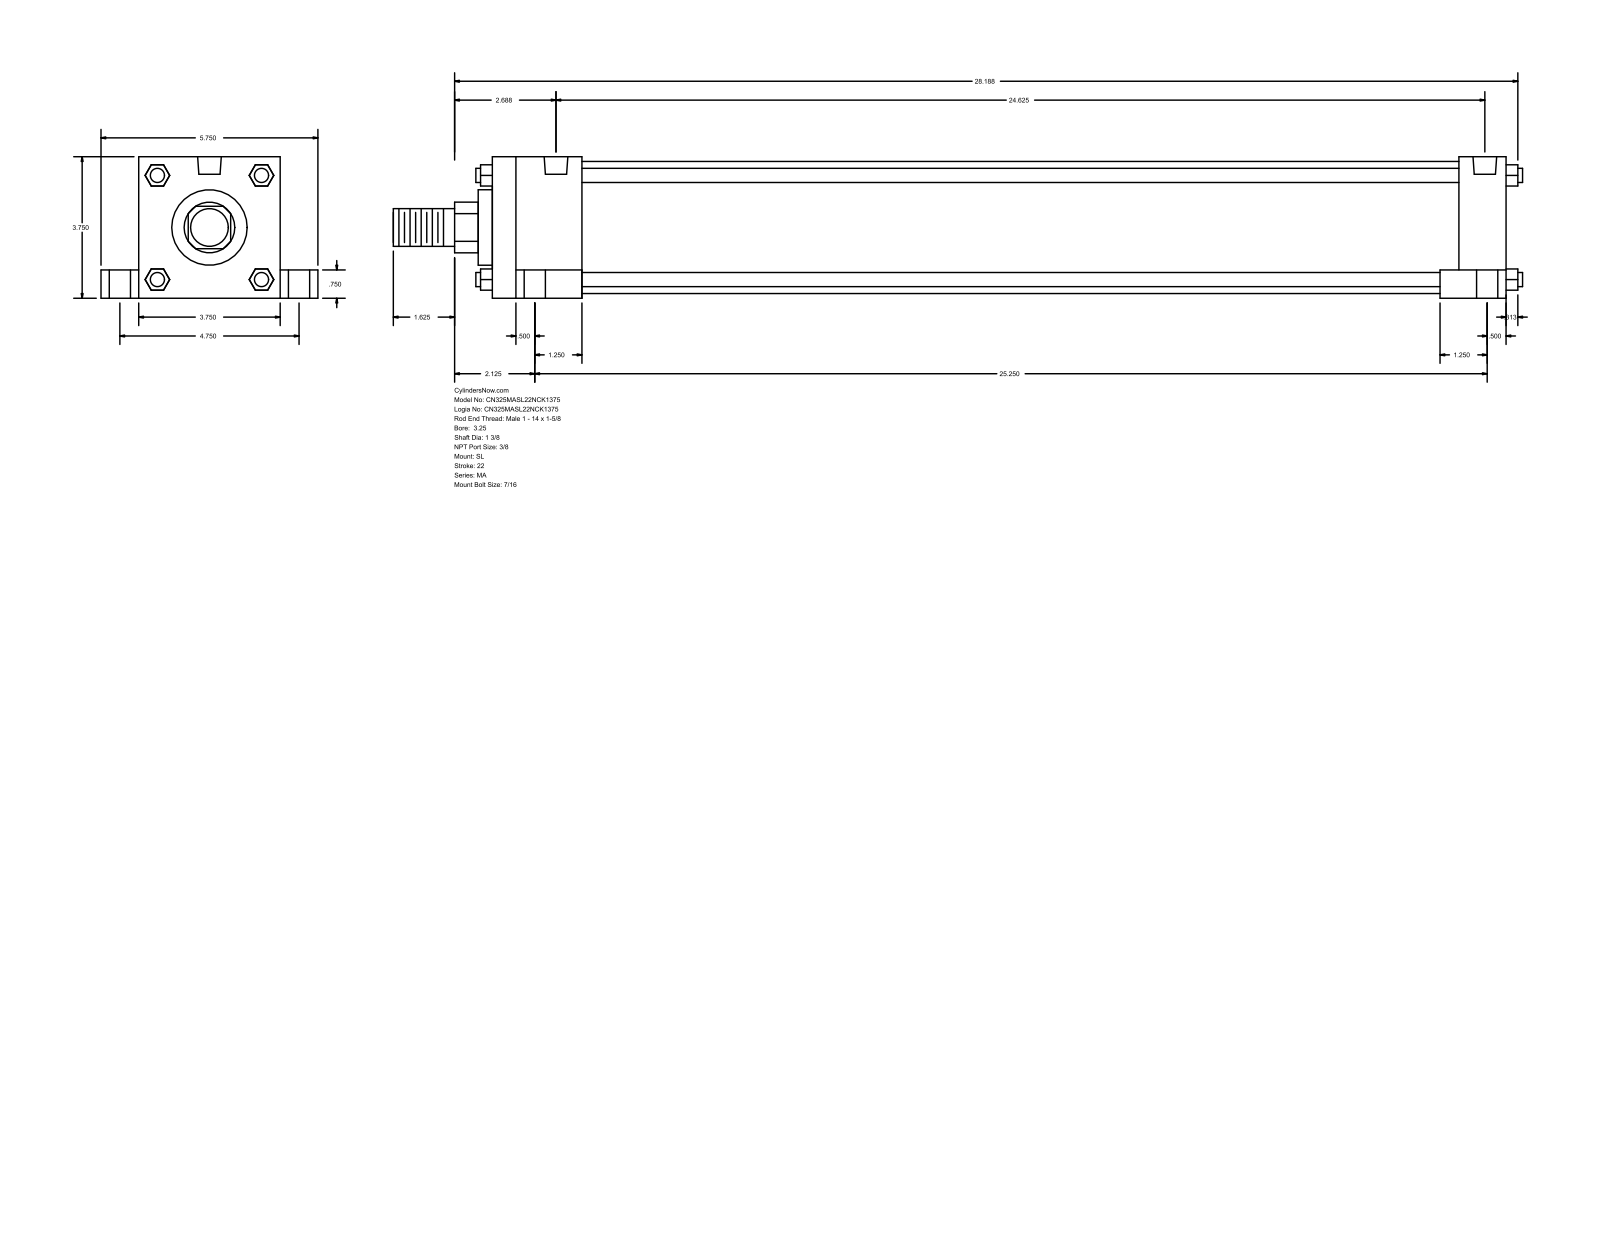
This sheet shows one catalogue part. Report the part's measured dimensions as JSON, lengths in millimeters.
{"part_name": "MA_SL__0325_1.375", "step_written_by": "GSSL Pune (CONFIG_CONTROL_DESIGN)", "units": "millimeters", "bodies": {"solids": 0, "faces": 148, "planar": 112, "cylindrical": 36, "other": 0}, "overall_size": [760.41, 146.05, 95.25], "round_holes": [[11.11, 4], [14.29, 4], [20.64, 4], [15.93, 2]], "round_bosses_or_shafts": [[9.53, 4], [88.9, 1], [50.8, 1], [34.92, 1], [25.4, 1]], "partial_cylinders_radius": [[17.06, 1]], "face_to_face_distances": [95.24, 682.62, 590.55, 25.41, 120.65, 650.87, 31.75, 60.32, 622.3, 19.05], "hole_center_spacings": [60.35, 60.66, 62, 63.27, 120.66, 615.95, 625.22, 629.97]}
